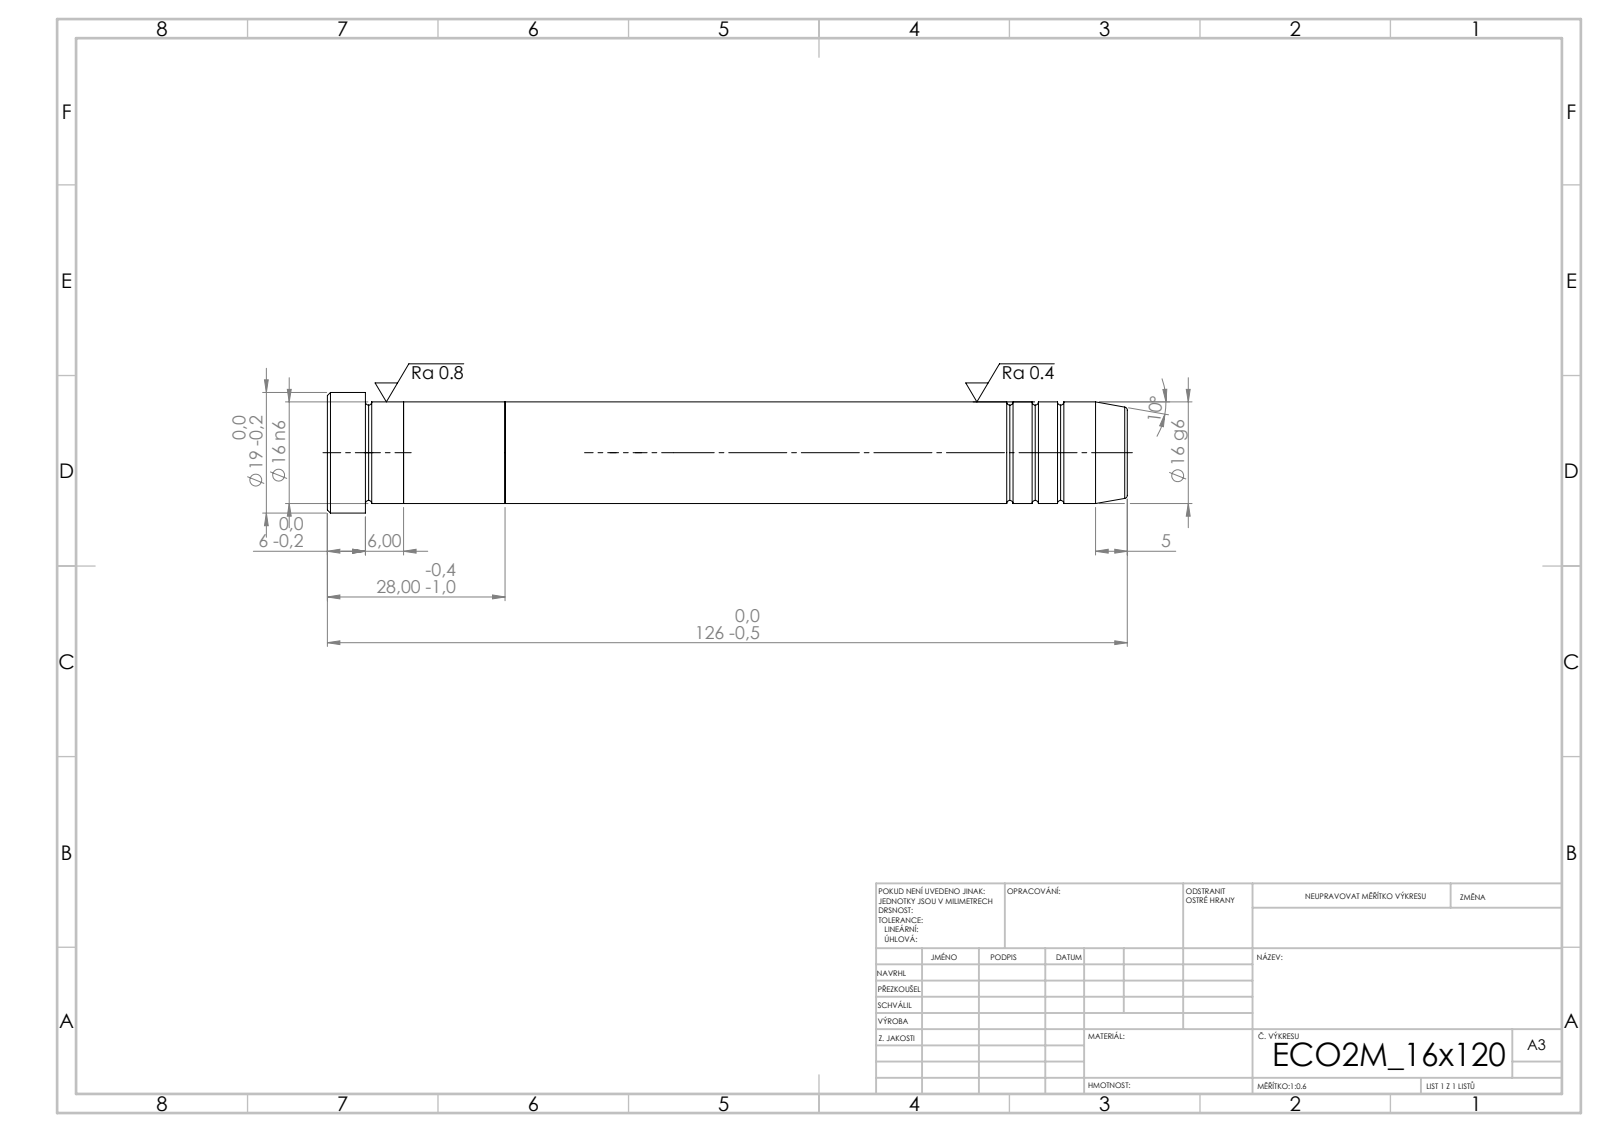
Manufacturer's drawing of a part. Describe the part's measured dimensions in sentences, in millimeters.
Its 3-D file was written by "SolidWorks 2019 (CONFIG_CONTROL_DESIGN)". It is 3 solids with 43 faces: 7 planar, 14 cylindrical and 22 other. Overall it measures 126 by 19 by 19 millimeters. Its volume is 25 636 cubic millimeters and its surface area 7 787 square millimeters. Round bosses or shafts: 1 of diameter 19, 1 of diameter 16. The main face-to-face distances are 16, 28, 12, 6, 98, 114, 126, 120, 22.
